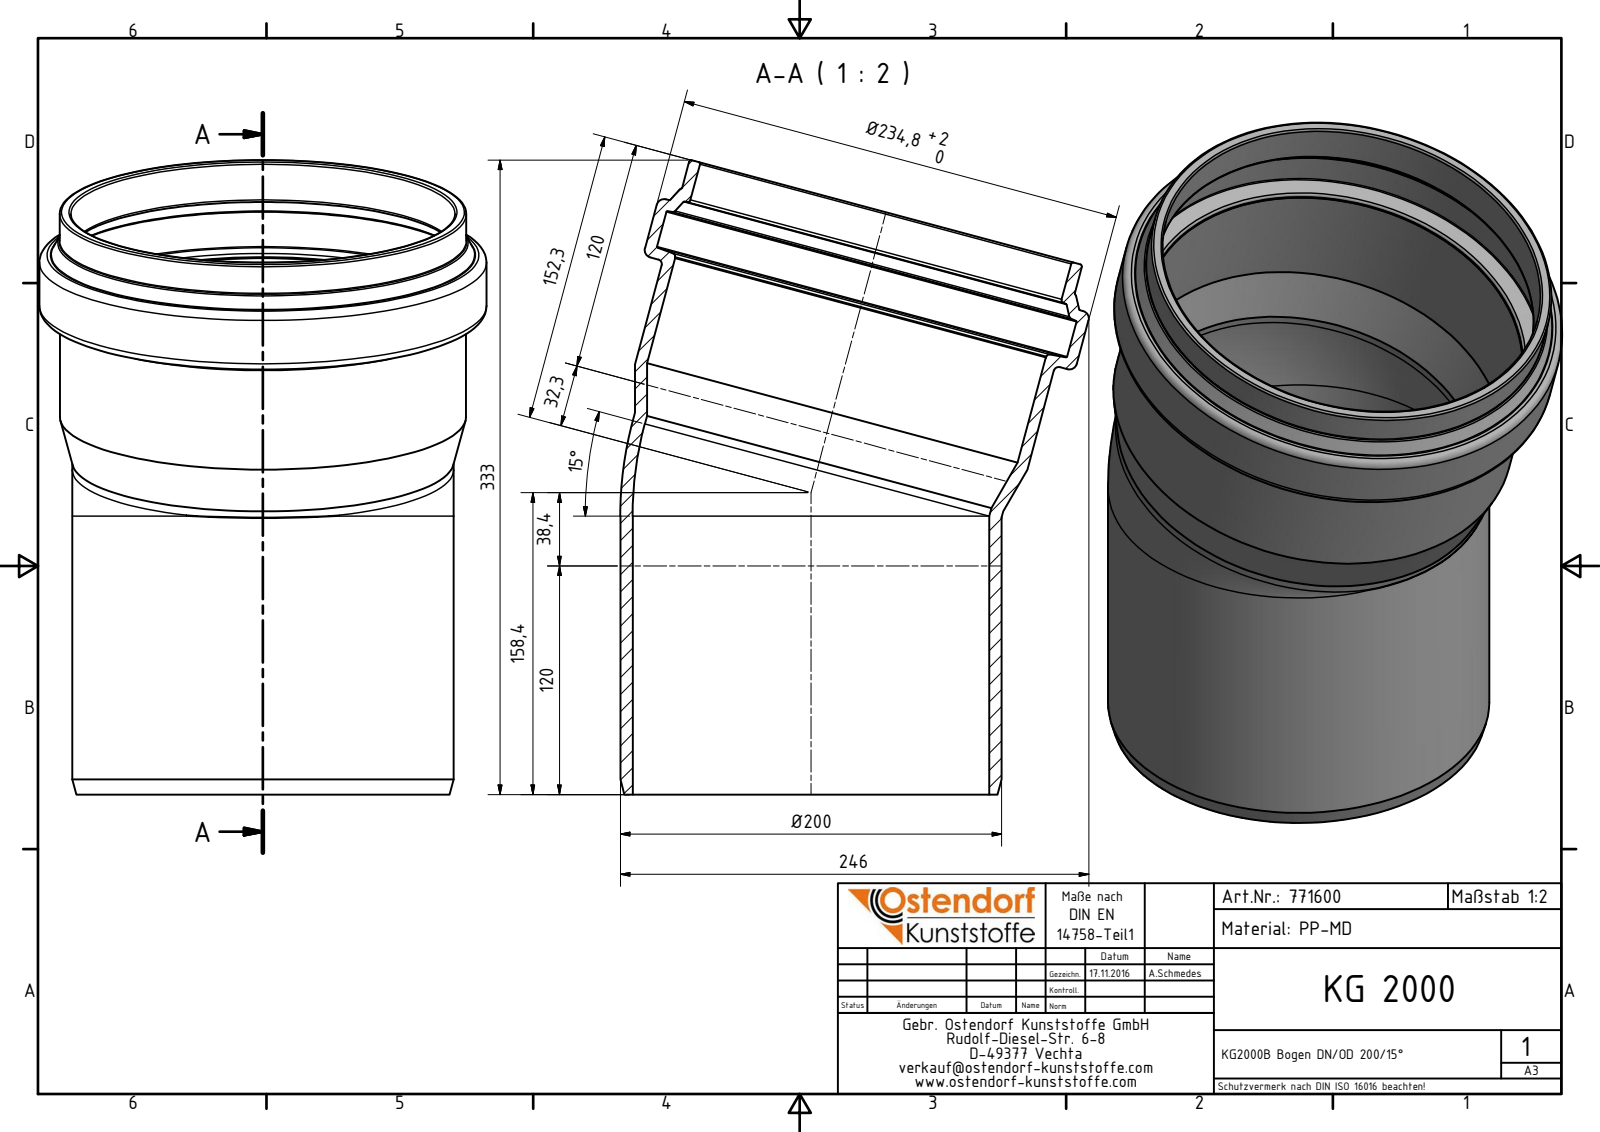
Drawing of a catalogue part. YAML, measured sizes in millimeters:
part_name: "771600 KG2000B Bogen DN_OD 200_15°"
step_written_by: "Autodesk Inventor 2016 (AUTOMOTIVE_DESIGN)"
units: millimeters
bodies: {solids: 1, faces: 41, planar: 5, cylindrical: 11, other: 25}
overall_size: [333, 246, 234.8]
volume: 1284000
surface_area: 419653
round_holes:
  - {diameter: 187.2, count: 2}
  - {diameter: 201.8, count: 2}
  - {diameter: 201.5, count: 1}
  - {diameter: 223, count: 1}
round_bosses_or_shafts:
  - {diameter: 200.2, count: 2}
  - {diameter: 234.8, count: 1}
  - {diameter: 213.6, count: 1}
  - {diameter: 213.3, count: 1}
face_to_face_distances: [54.9, 31.6, 23.3, 3.02, 28.58, 51.88]
